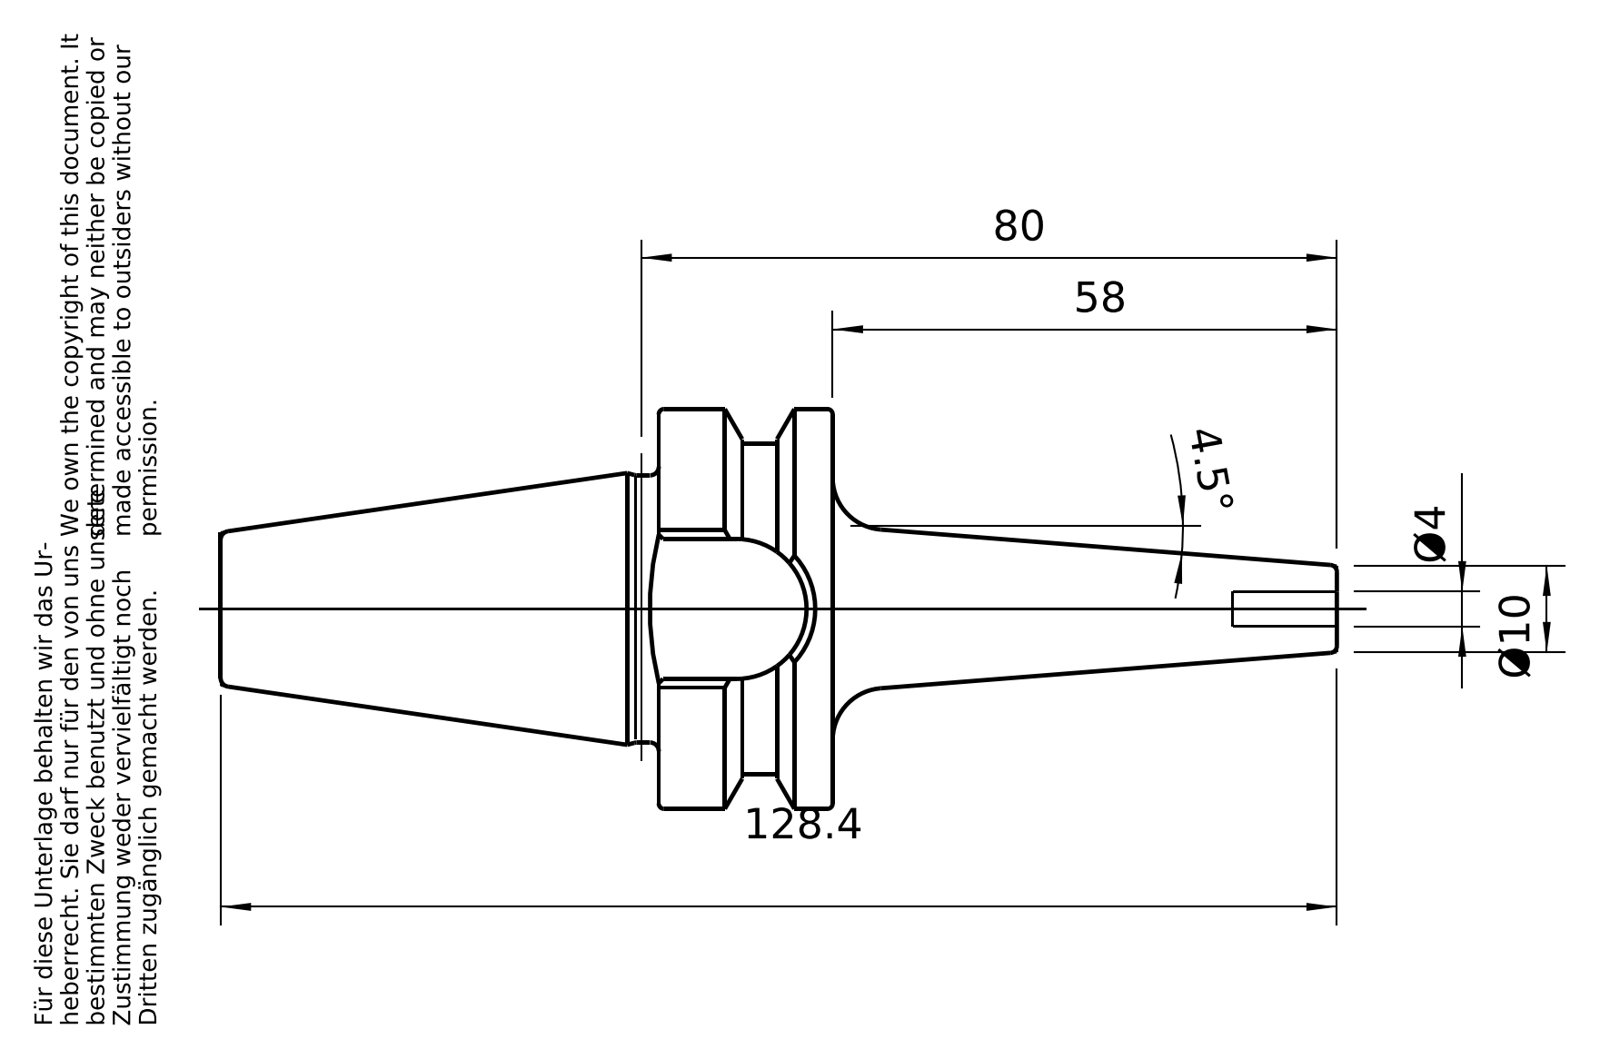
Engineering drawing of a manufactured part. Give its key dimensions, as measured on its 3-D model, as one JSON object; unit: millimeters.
{"part_name": "30-640-04", "step_written_by": "PRO/ENGINEER BY PARAMETRIC TECHNOLOGY CORPORATION, 2010430 (CONFIG_CONTROL_DESIGN)", "units": "millimeters", "bodies": {"solids": 1, "faces": 94, "planar": 26, "cylindrical": 20, "other": 48}, "overall_size": [128.4, 45.98, 45.98], "volume_mm3": 59779, "surface_area_mm2": 14325, "round_holes": [[4, 1], [10.11, 1], [12.51, 1], [13, 1]], "round_bosses_or_shafts": [[45.98, 1], [30.75, 1], [12.01, 1]], "partial_cylinders_radius": [[8.1, 1], [18.88, 1]], "face_to_face_distances": [20, 32.3, 16.2, 50.4, 70.4, 128.4, 78, 58, 25, 25.4]}
